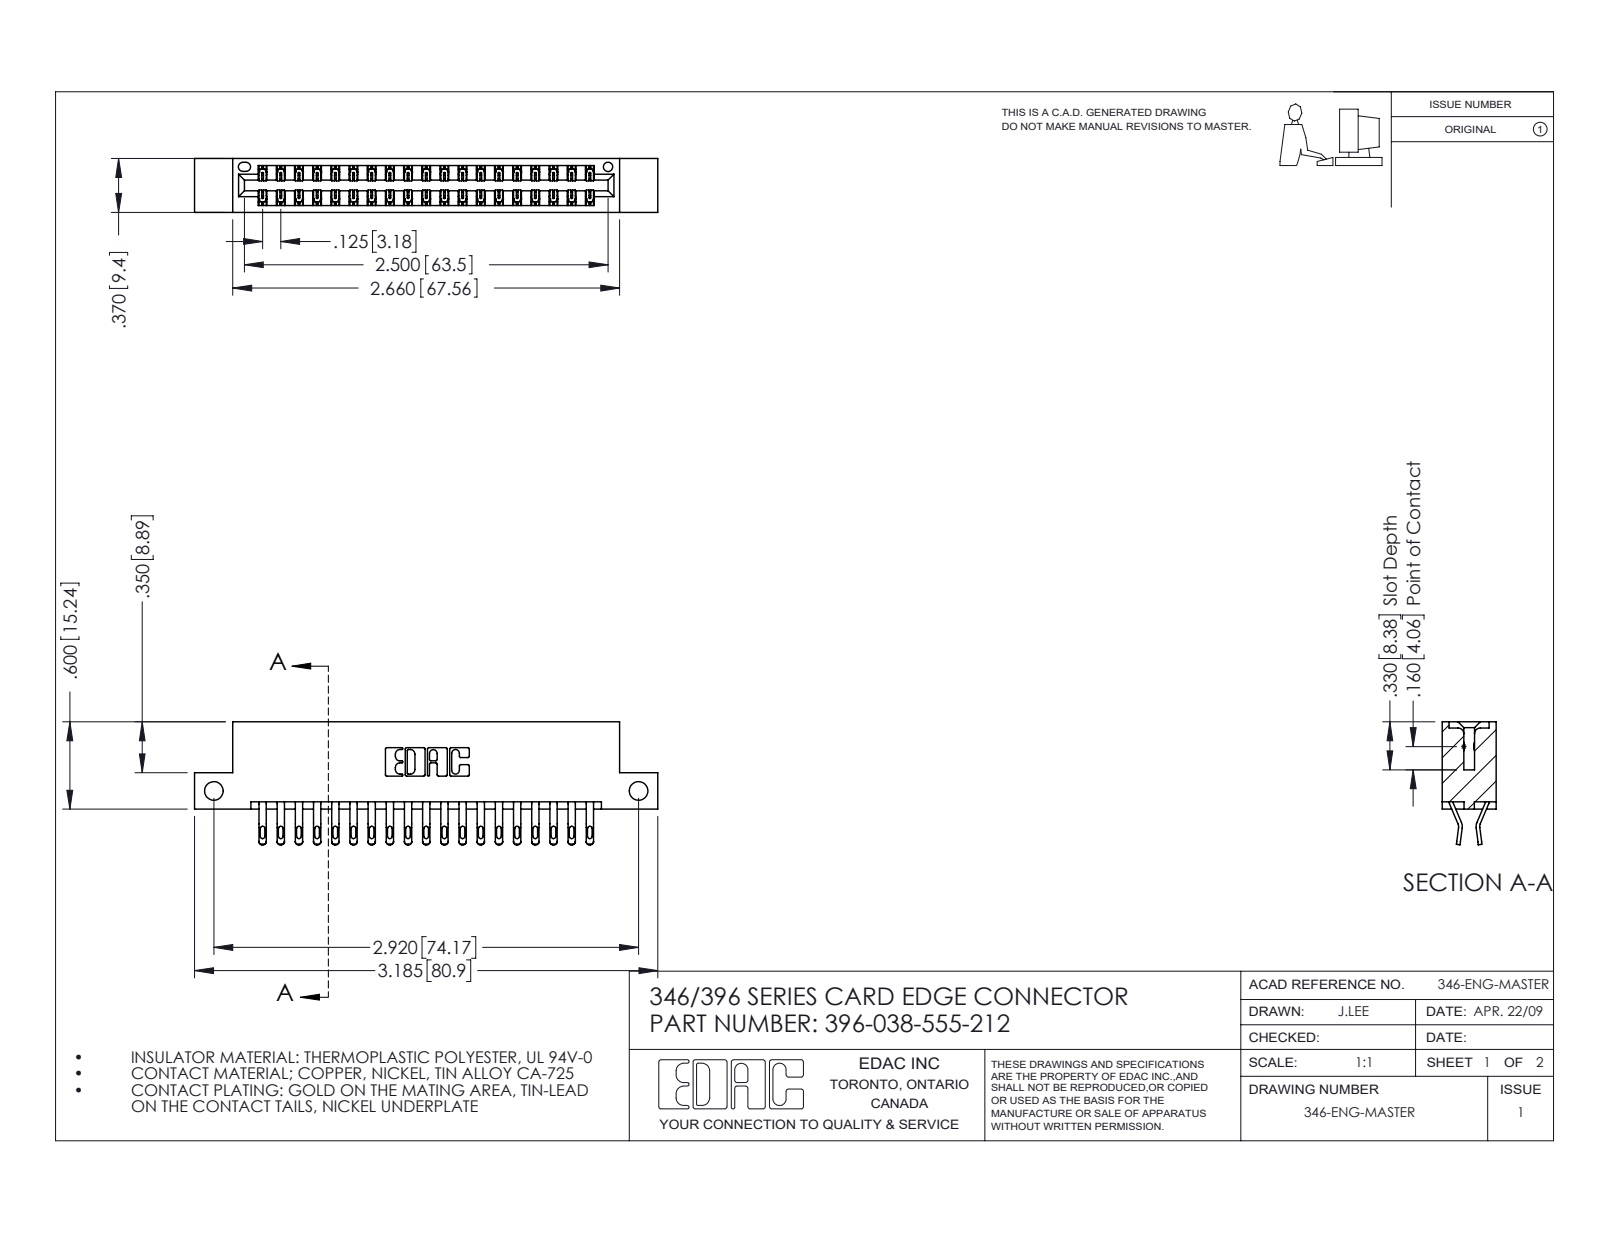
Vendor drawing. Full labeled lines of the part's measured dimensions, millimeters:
Part name (STEP PRODUCT): 346 Part_Flush Mounting Lugs - Side Mount; 396-038-555-212; 345-292-001_555 Tail
STEP written by: SolidWorks 2016 (CONFIG_CONTROL_DESIGN)
Units: millimetres
Bodies: 39 solids, 2326 faces (1330 planar, 996 cylindrical, 0 other)
Overall size (bounding box): 80.9 × 21.5 × 9.4
Volume: 7 730 mm³ · Surface area: 10 520 mm²
Round holes (diameter × count): ⌀3.3 ×2, ⌀1.6 ×1
Partial cylindrical surfaces — rounded edges, fillets, slot ends (radius × count): R0.4 ×76, R0.5 ×76, R0.2 ×57, R0.3 ×22, R0.2 ×6, R0.8 ×6, R0.7 ×3, R0.3 ×2
Main face-to-face distances: 1.2, 8.2, 6.4, 9.4, 0.6, 1.8, 7.6, 7, 3.8, 5.6
Hole centre spacings: 74.2
